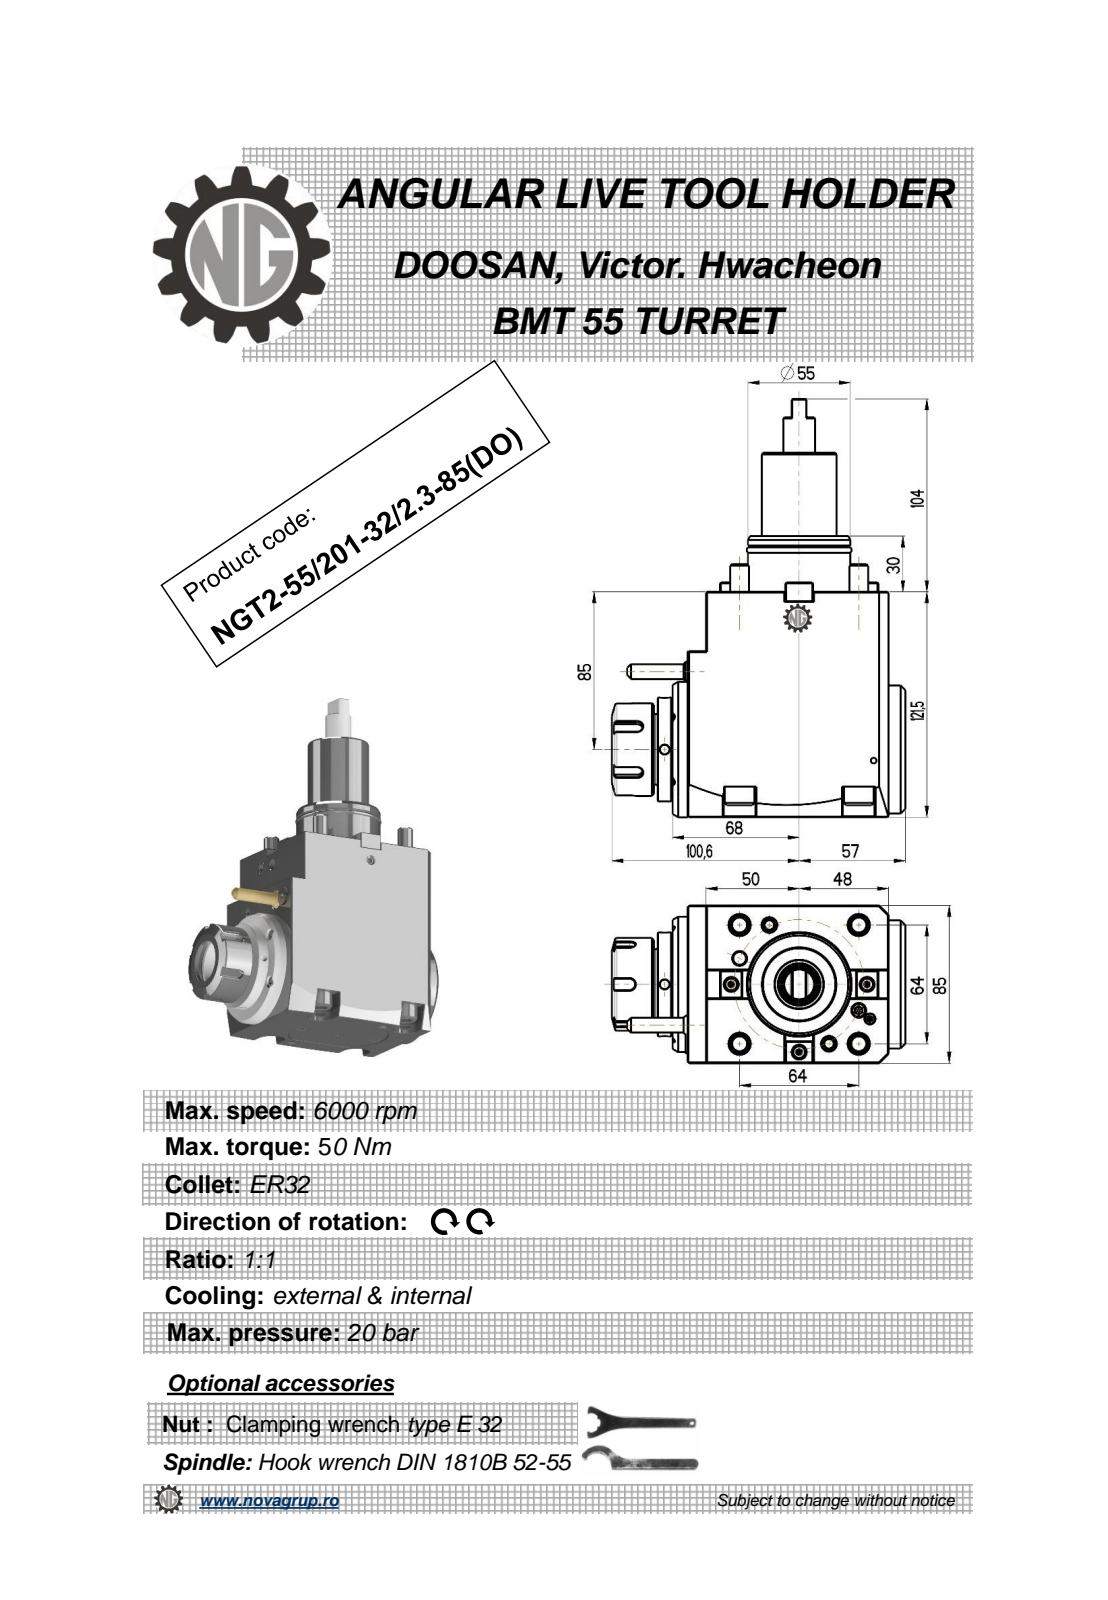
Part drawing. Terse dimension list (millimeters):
name: NGT2_55_201_32_1_3_85_DO
written by: PRO/ENGINEER BY PARAMETRIC TECHNOLOGY CORPORATION, 2010280 (CONFIG_CONTROL_DESIGN)
unit: mm
bodies: 2 solids, 495 faces (241 planar, 117 cylindrical, 137 other)
size: 225.5 × 158.9 × 85
volume: 1 329 000 mm³; area: 115 386 mm²
holes: 3× ⌀5, 2× ⌀6.8, 1× ⌀3, 1× ⌀12, 1× ⌀27
bosses: 4× ⌀16, 4× ⌀10, 2× ⌀50, 1× ⌀73, 1× ⌀68, 1× ⌀56, 1× ⌀55, 1× ⌀43.4
rounds: 20× R0.32, 6× R0.22, 6× R0.31, 5× R3, 4× R8.5, 2× R0.8, 2× R480
face distances: 85, 121.5, 8, 10, 108, 118.3, 10.3, 18, 98, 108.3
hole spacings: 42.62, 47.41, 69.86, 105.19
